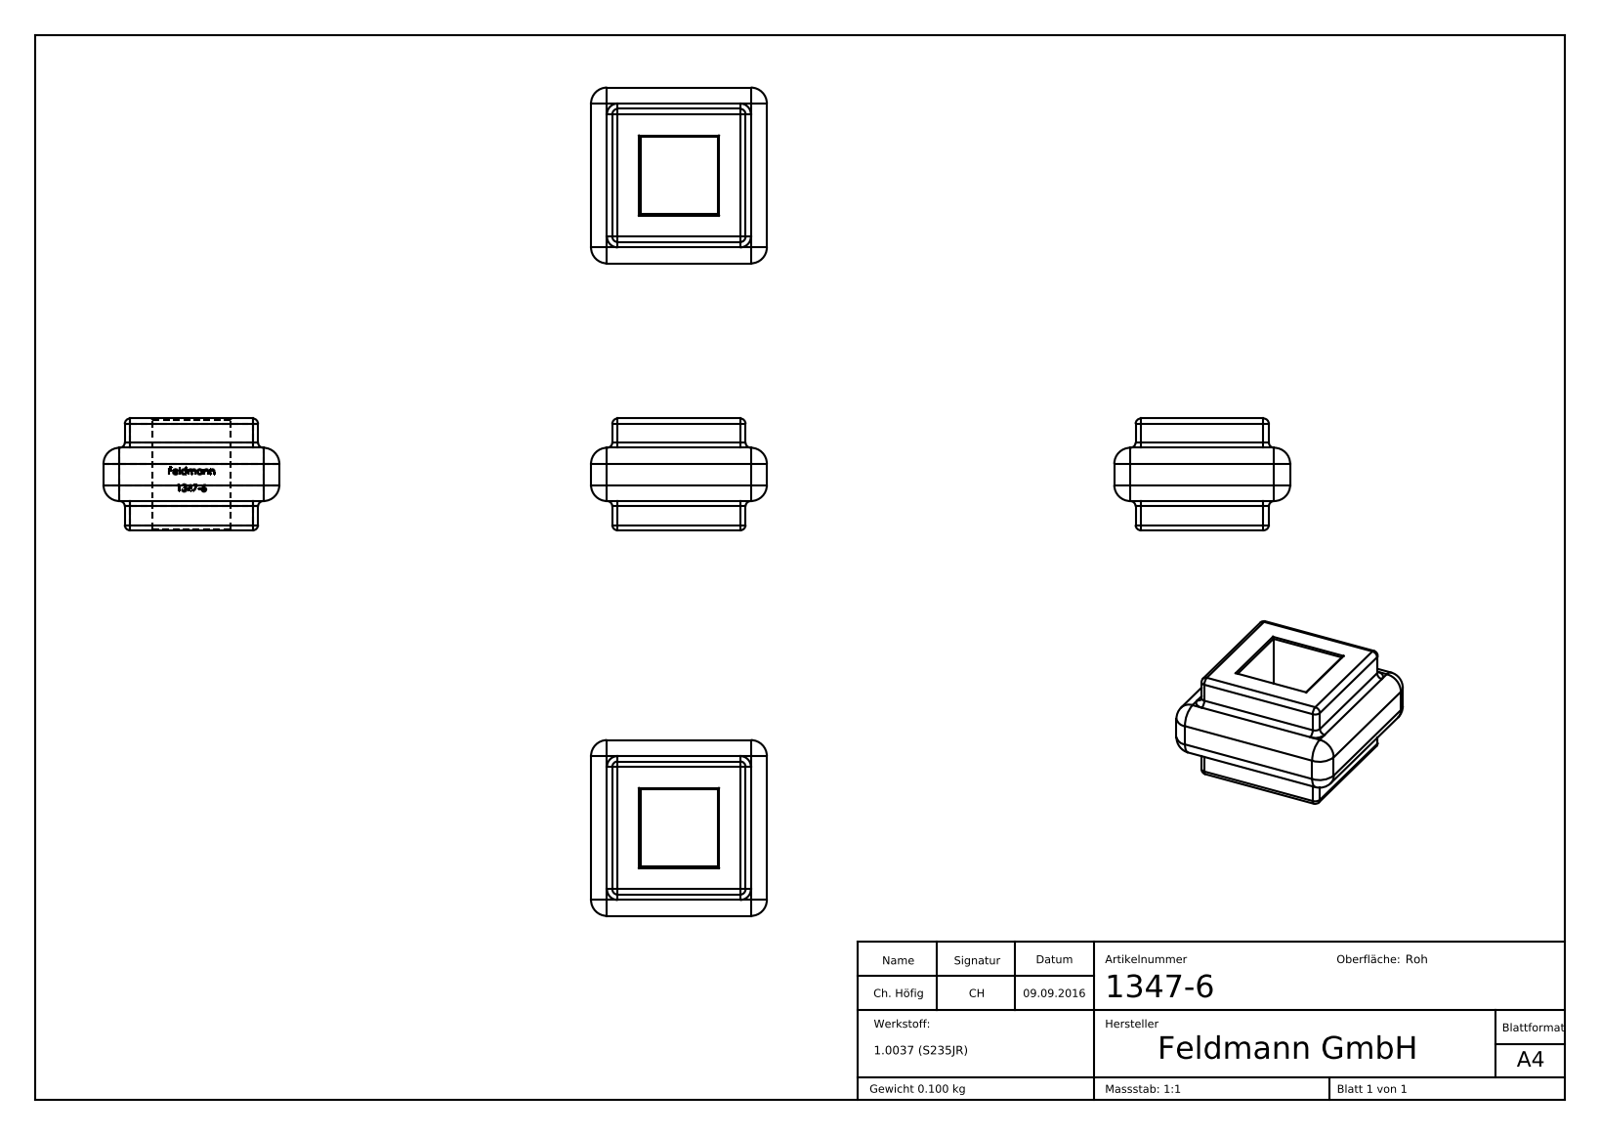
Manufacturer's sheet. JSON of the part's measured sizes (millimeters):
{"part_name": "1347-6", "step_written_by": "SolidWorks 2015 (CONFIG_CONTROL_DESIGN)", "units": "millimeters", "bodies": {"solids": 1, "faces": 273, "planar": 142, "cylindrical": 36, "other": 95}, "overall_size": [33, 33, 21], "volume_mm3": 12786, "surface_area_mm2": 4797, "partial_cylinders_radius": [[1, 20], [3, 12]], "face_to_face_distances": [5.25, 19.75, 14.5, 4, 9.25, 23.75, 29, 25, 21, 33]}
